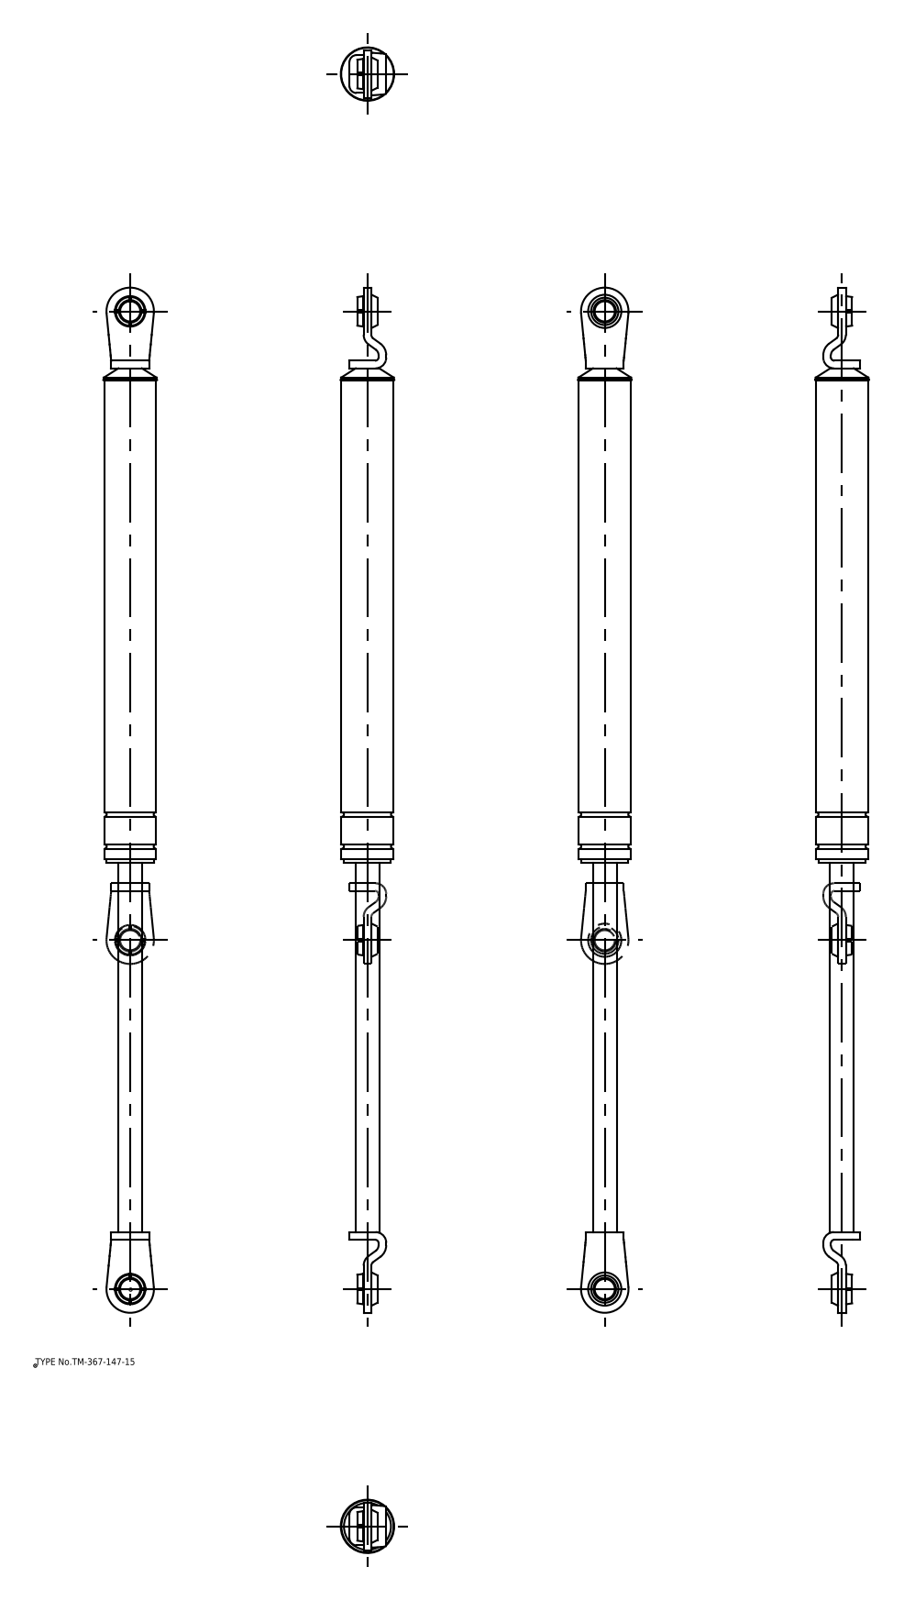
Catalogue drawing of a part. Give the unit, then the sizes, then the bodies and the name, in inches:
Units: inches
Overall size (bounding box): 17.008 × 0.886 × 0.886
Round holes (diameter × count): ⌀0.335 ×2
Round bosses / shafts (diameter × count): ⌀0.476 ×2, ⌀0.866 ×1, ⌀0.78 ×1, ⌀0.394 ×1
Partial cylindrical surfaces — rounded edges, fillets, slot ends (radius × count): R0.118 ×4, R0.059 ×2, R0.079 ×2, R0.177 ×2, R0.197 ×2, R0.236 ×2, R0.394 ×2
Main face-to-face distances: 0.126, 14.457, 0.23, 0.132, 0.236, 6.248, 14.583, 8.335, 0.104, 8.209
Hole centre spacings: 16.22
Volume: 5.851 in³ · Surface area: 38.16 in²
Bodies: 2 solids, 153 faces (79 planar, 40 cylindrical, 34 other)
Part name (STEP PRODUCT): TM-367_147_15; TM-367_147_15_div
STEP written by: spGate 16.7.1 (AUTOMOTIVE_DESIGN)
